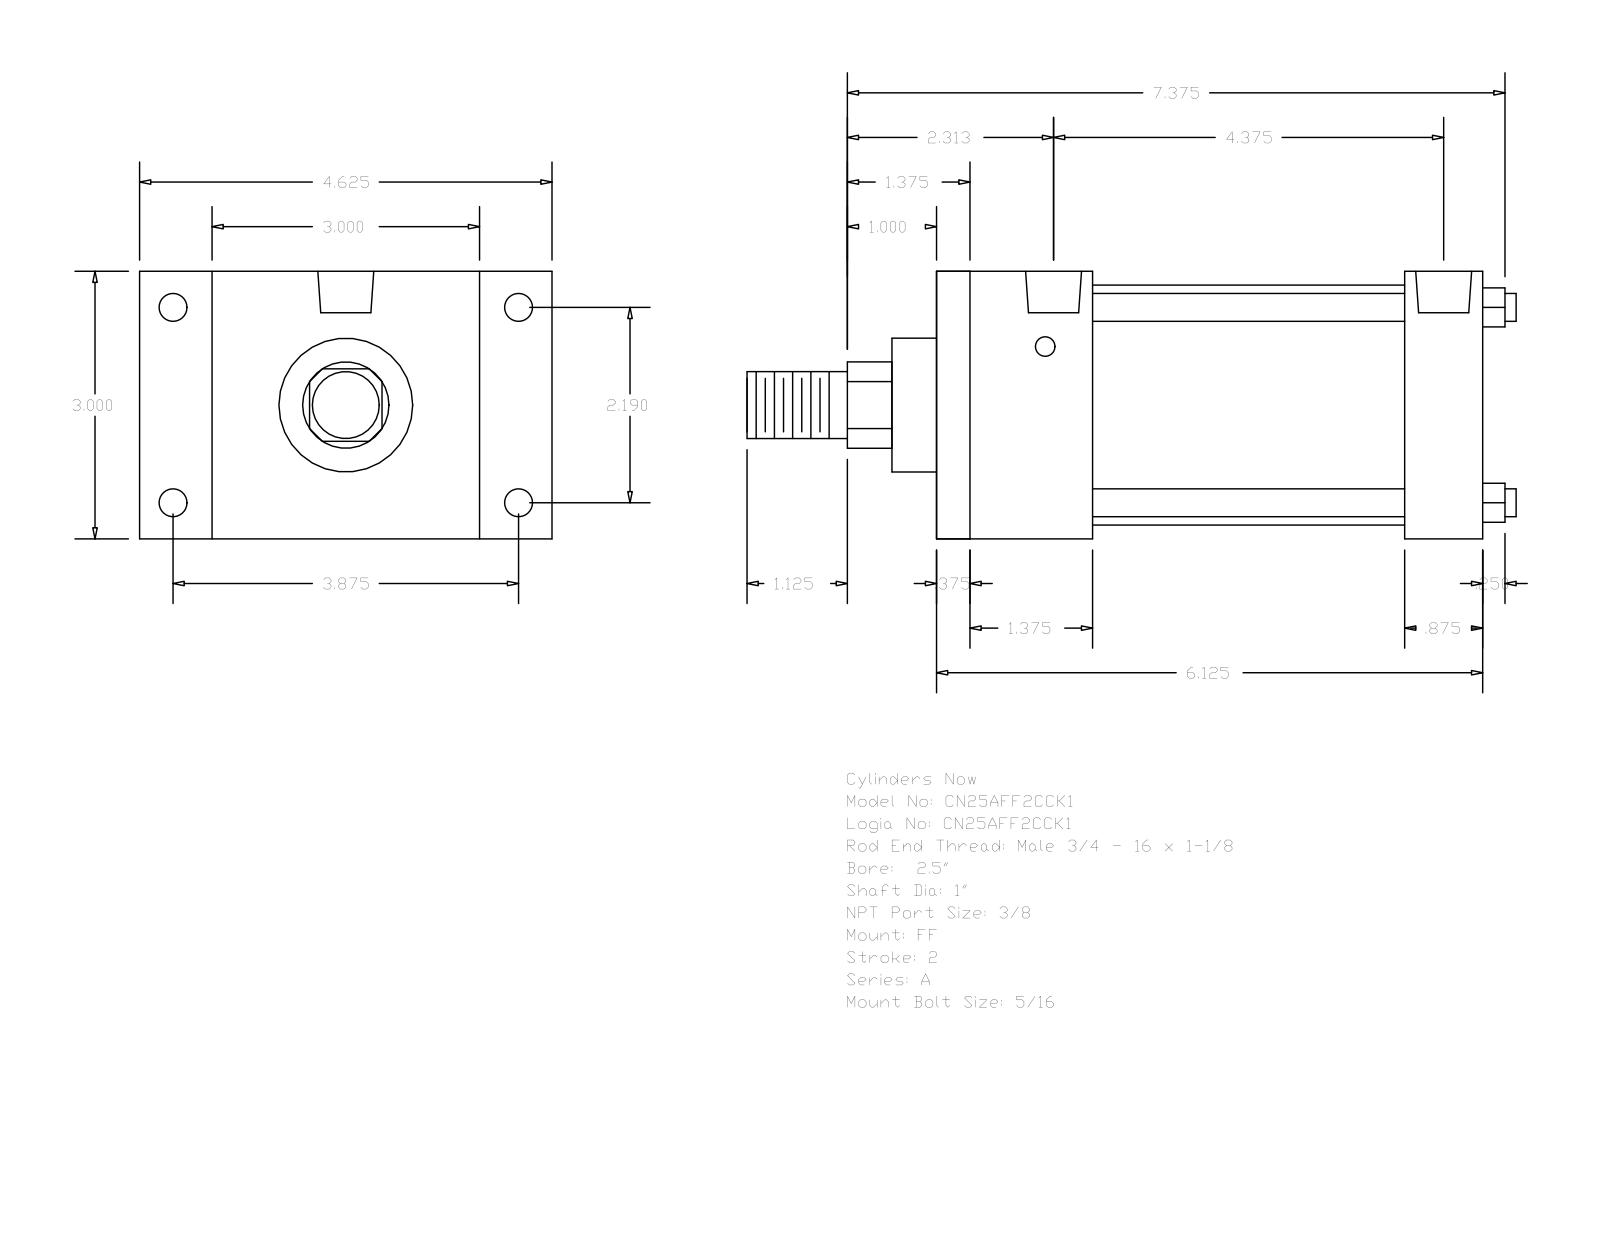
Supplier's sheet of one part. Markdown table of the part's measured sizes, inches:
| quantity | value |
| --- | --- |
| part name | A_FF__0250_1 |
| STEP written by | GSSL Pune (CONFIG_CONTROL_DESIGN) |
| units | inches |
| bodies | 0 solids, 92 faces (64 planar, 28 cylindrical, 0 other) |
| overall size | 8.625 × 4.625 × 3 |
| round holes (diameter × count) | 0.219 × 4, 0.313 × 4, 0.627 × 2 |
| round bosses / shafts (diameter × count) | 0.313 × 4, 2.69 × 1, 1.5 × 1, 1 × 1, 0.75 × 1 |
| partial cylindrical surfaces (radius × count) | 0.484 × 1 |
| main face-to-face distances | 3, 6.125, 5.75, 0.375, 0.875, 1.75, 5.25, 1.375, 4.875, 3.5 |
| hole center spacings | 0.094, 2.19, 3.875, 4.451, 4.469, 4.562, 4.375 |
